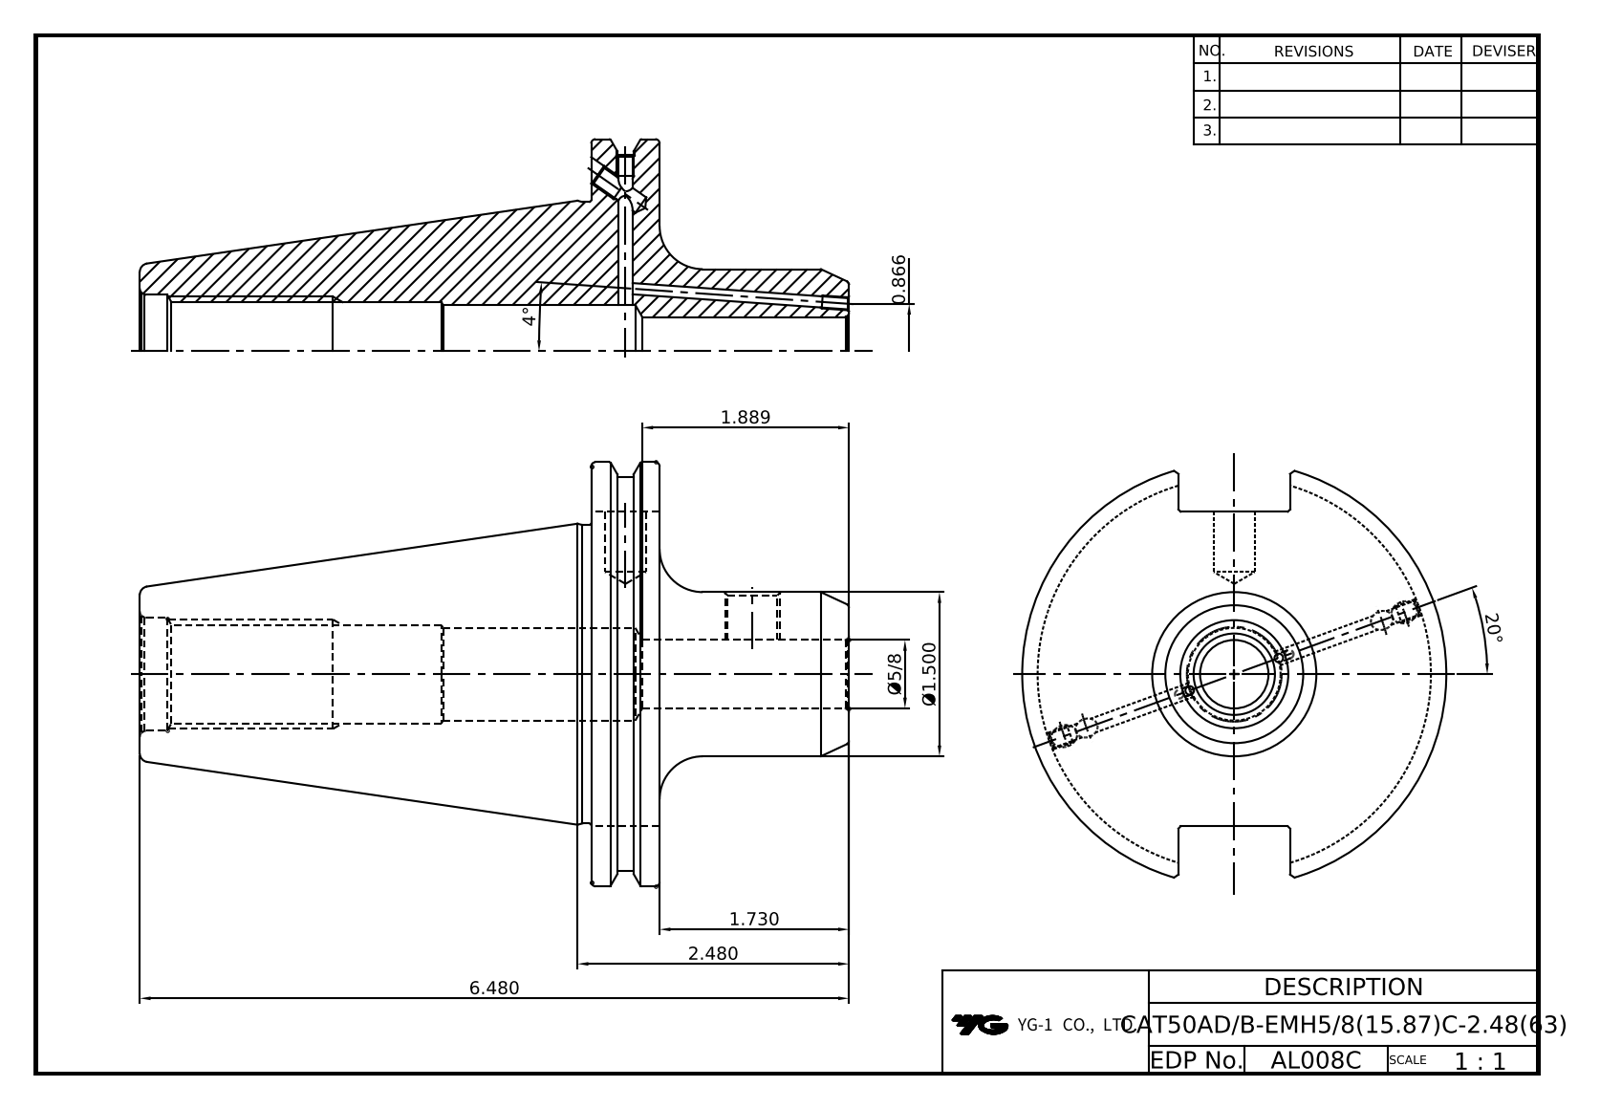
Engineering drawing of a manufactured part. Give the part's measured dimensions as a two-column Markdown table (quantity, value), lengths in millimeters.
| quantity | value |
| --- | --- |
| part name | LO-CAT50ADB-EMH15.875C-63 |
| STEP written by | Autodesk Inventor 2025 (AUTOMOTIVE_DESIGN) |
| units | millimeters |
| bodies | 1 solid, 88 faces (37 planar, 27 cylindrical, 24 other) |
| overall size | 164.6 × 98.42 × 94.69 |
| volume | 359 319 mm³ |
| surface area | 52 857 mm² |
| round holes (diameter × count) | 2.46 × 2, 3.24 × 2, 4.13 × 2, 4.2 × 2, 5 × 2, 9.53 × 1, 11.33 × 1, 15.88 × 1, 21.97 × 1, 26.2 × 1 |
| round bosses / shafts (diameter × count) | 98.42 × 1, 91.29 × 1, 69.25 × 1, 38.1 × 1 |
| main face-to-face distances | 15.88, 104.77, 120.65, 164.6, 59.83, 43.95, 73.03, 25.9, 114.64, 9.87 |
| hole center spacings | 29.47 |
